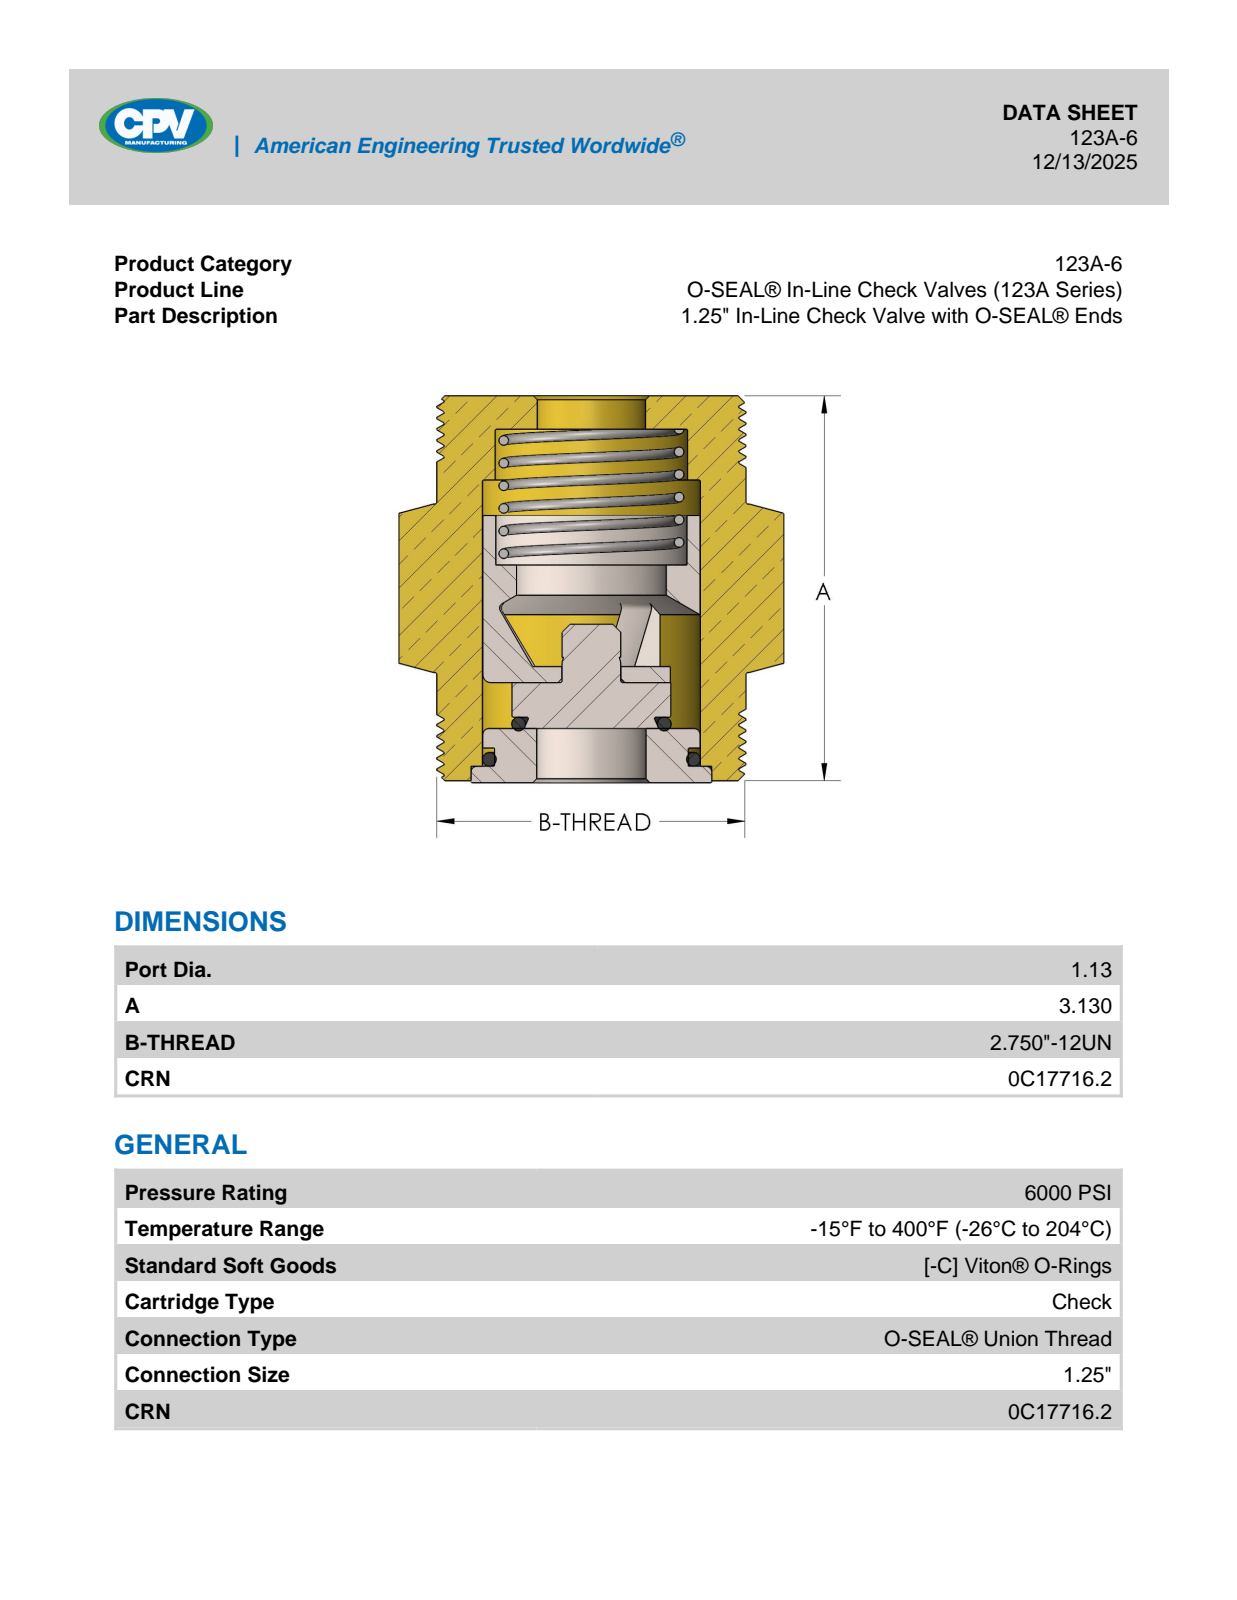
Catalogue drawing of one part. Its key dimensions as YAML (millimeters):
part_name: "123A-6"
step_written_by: "SolidWorks 2018 (AUTOMOTIVE_DESIGN)"
units: millimeters
bodies: {solids: 1, faces: 65, planar: 11, cylindrical: 38, other: 16}
overall_size: [82.6, 79.9, 74.7]
volume: 338700
surface_area: 34920
round_holes:
  - {diameter: 28.6, count: 1}
  - {diameter: 30.2, count: 1}
round_bosses_or_shafts:
  - {diameter: 69.7, count: 1}
  - {diameter: 52.1, count: 1}
partial_cylinders:
  - {radius: 41.3, count: 1}
face_to_face_distances: [79.9, 0.4, 79.5, 74.7, 21, 59.3, 20.6, 58.9, 38.4, 58.9]
